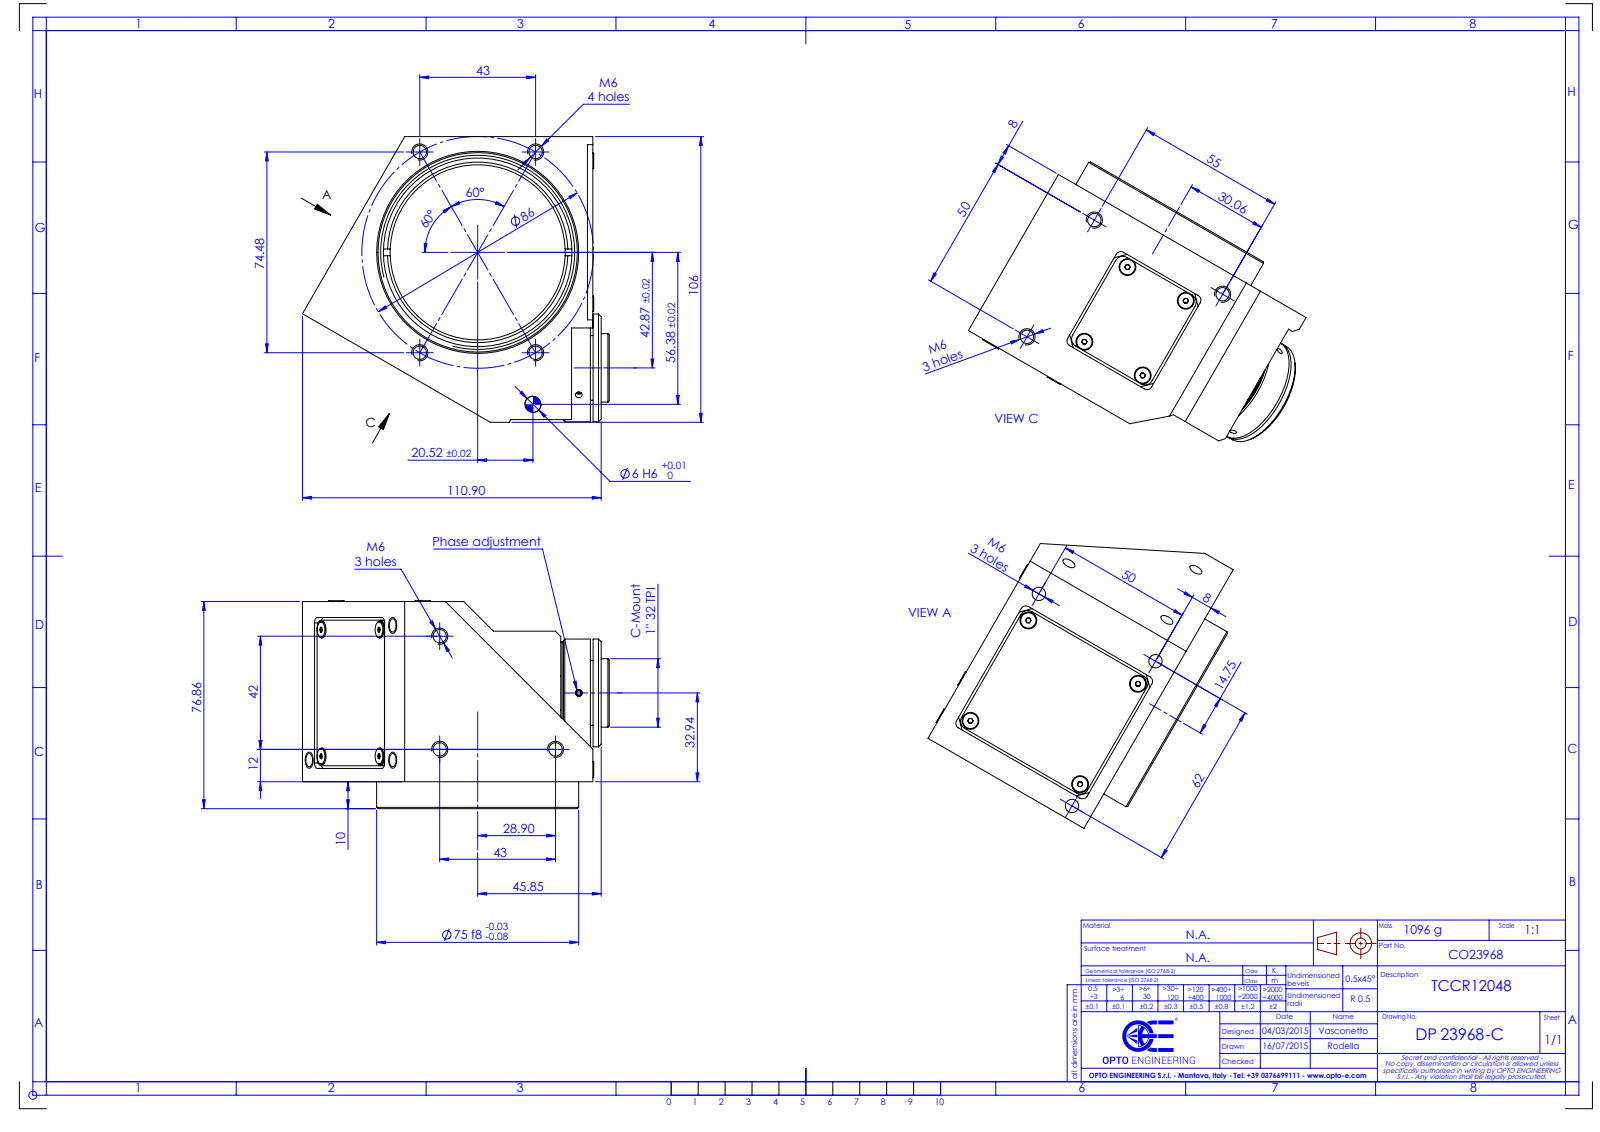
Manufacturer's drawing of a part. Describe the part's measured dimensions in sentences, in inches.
The part is named "DP23968_TCCR12048". Its 3-D file was written by "SolidWorks 2021 (CONFIG_CONTROL_DESIGN)". It is 0 solids with 285 faces: 117 planar, 100 cylindrical and 68 other. Overall it measures 4.484 by 4.173 by 3.039 inches. Round holes: 13 of diameter 0.197, 3 of diameter 0.098, 1 of diameter 0.236, 1 of diameter 0.571, 1 of diameter 0.866, 1 of diameter 0.886, 1 of diameter 2.559, 1 of diameter 2.756. Round bosses or shafts: 13 of diameter 0.226, 1 of diameter 2.953, 1 of diameter 1.575, 1 of diameter 1.504, 1 of diameter 1.488, 1 of diameter 1. Partial cylindrical surfaces (rounded edges, fillets, slot ends): 8 of radius 0.079, 8 of radius 0.118, 2 of radius 0.157. The main face-to-face distances are 0.02, 2.632, 0.039, 0.433, 0.177, 0.118, 2.677, 1.457, 4.134, 0.157. The hole center spacings are 1.693, 1.969, 2.932, 3.386, 0.755, 0.892, 1.654, 1.818.
